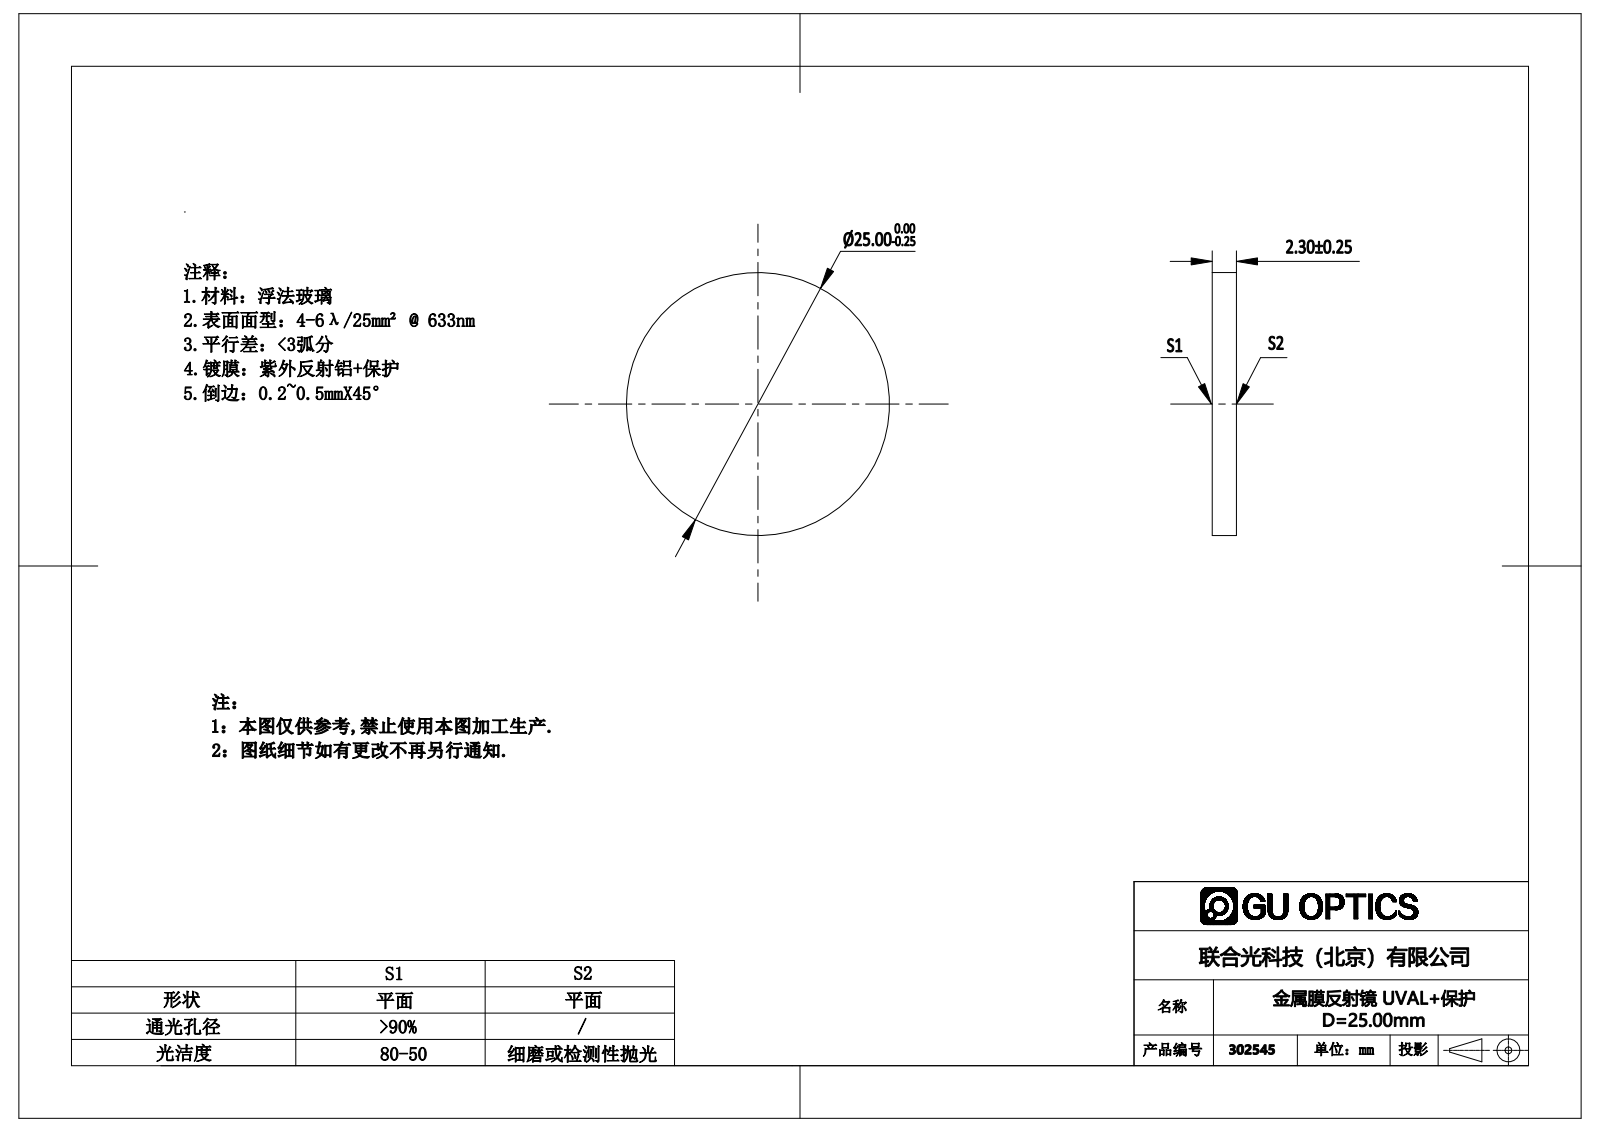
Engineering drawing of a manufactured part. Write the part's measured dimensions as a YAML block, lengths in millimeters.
part_name: "302516"
step_written_by: "SolidWorks 2016 (AUTOMOTIVE_DESIGN)"
units: millimeters
bodies: {solids: 1, faces: 4, planar: 2, cylindrical: 2, other: 0}
overall_size: [25, 25, 2.3]
volume: 1129
surface_area: 1162
round_bosses_or_shafts:
  - {diameter: 25, count: 1}
face_to_face_distances: [2.3]
